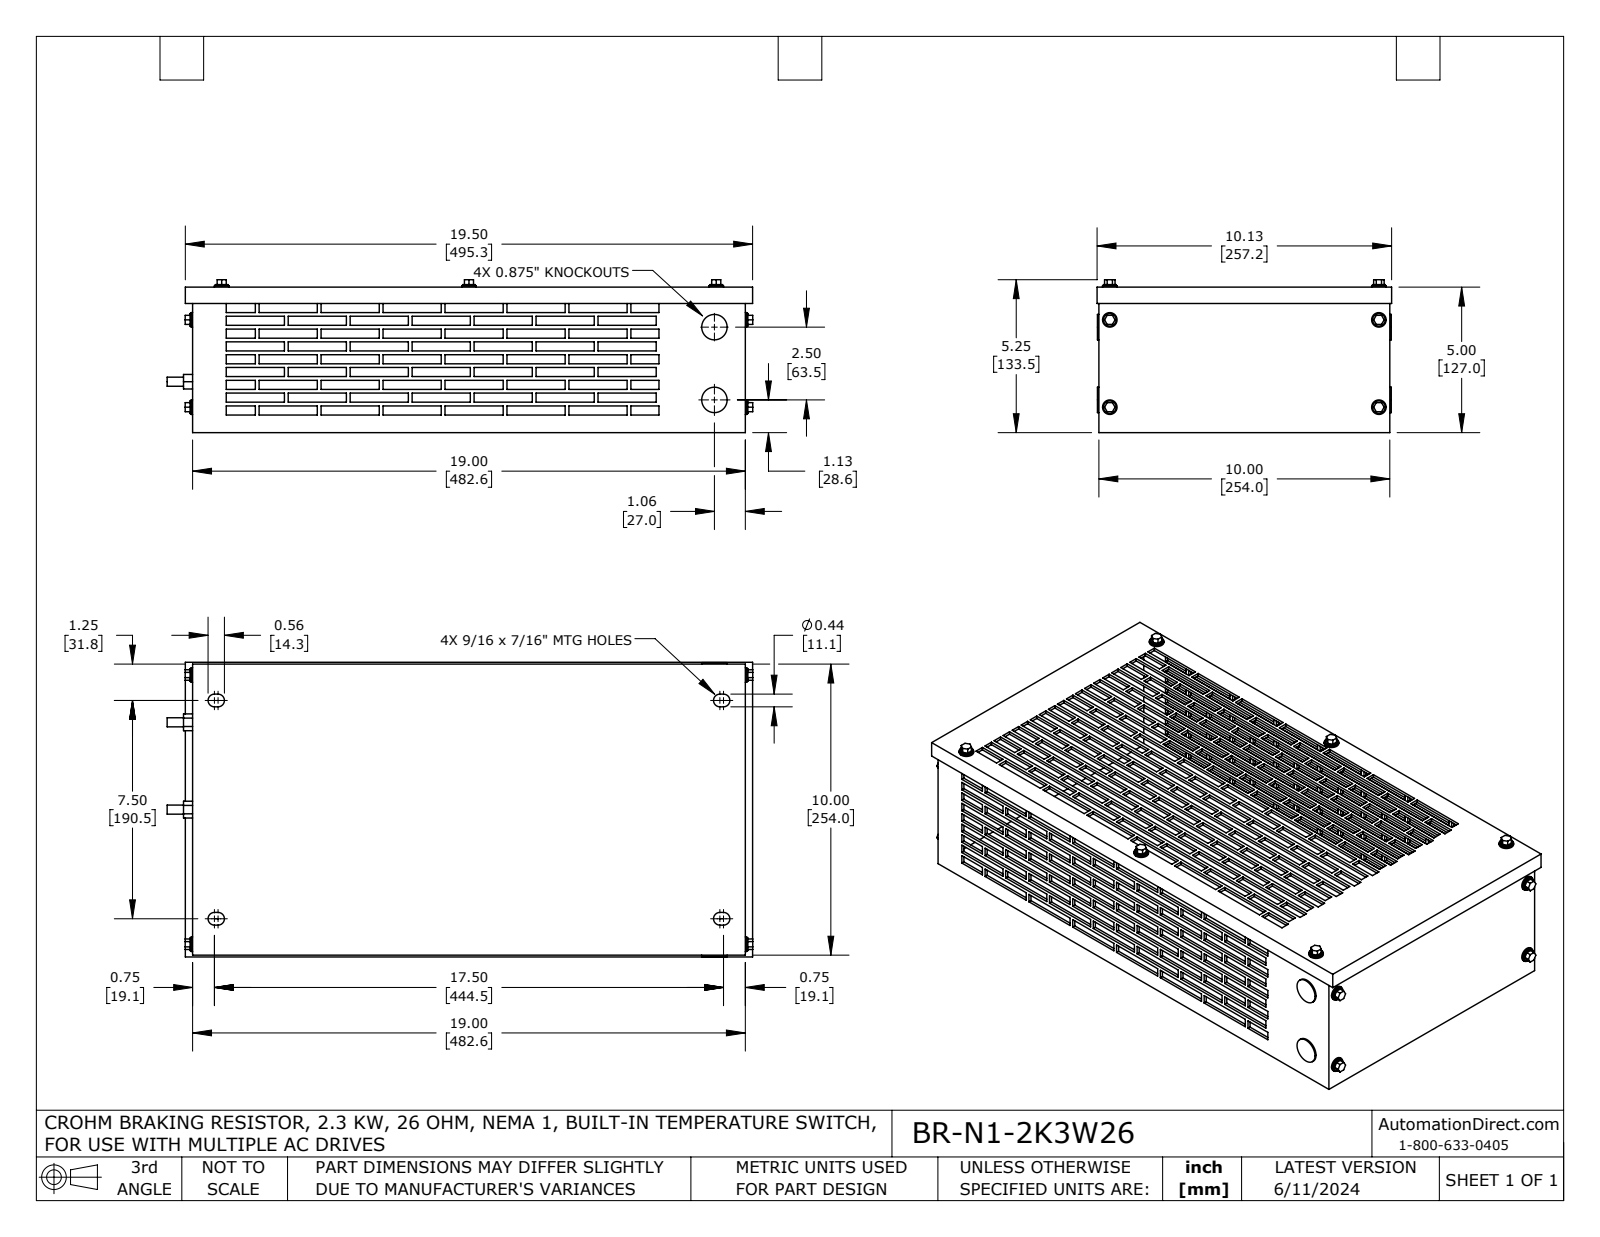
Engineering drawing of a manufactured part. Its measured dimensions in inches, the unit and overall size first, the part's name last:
Units: inches
Overall size (bounding box): 20.129 × 10.125 × 5.254
Round holes (diameter × count): ⌀0.25 ×10, ⌀0.75 ×2
Round bosses / shafts (diameter × count): ⌀0.5 ×10, ⌀0.437 ×10, ⌀0.875 ×2, ⌀0.313 ×2
Partial cylindrical surfaces — rounded edges, fillets, slot ends (radius × count): R0.219 ×8
Main face-to-face distances: 0.1, 4.9, 5, 4.8, 18.9, 9.9, 10, 19, 18.8, 9.8
Hole centre spacings: 9.25, 8.5, 12.562, 3, 9.724, 17, 19.354, 2.5
Volume: 51.07 in³ · Surface area: 1 155 in²
Bodies: 35 solids, 1454 faces (1342 planar, 112 cylindrical, 0 other)
Part name (STEP PRODUCT): BR-N1-2K3W26
STEP written by: SolidWorks 2021 (AUTOMOTIVE_DESIGN)
